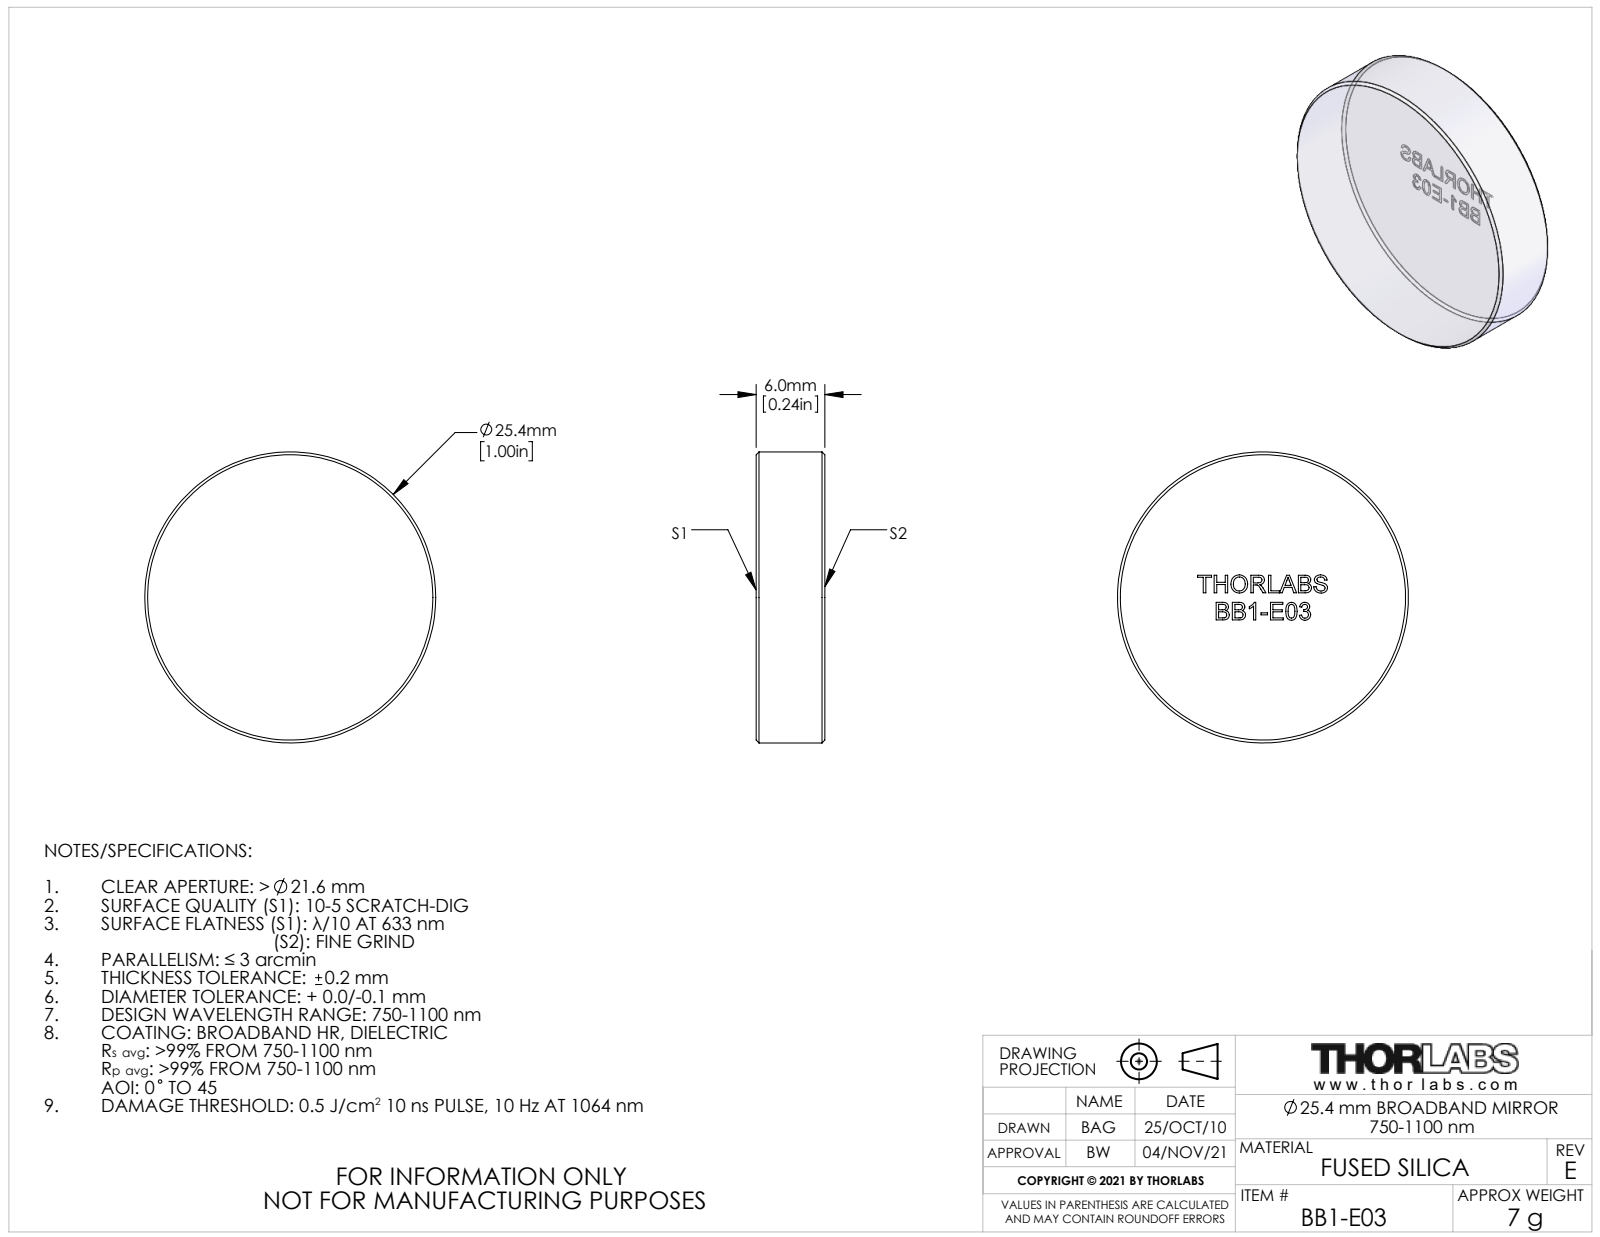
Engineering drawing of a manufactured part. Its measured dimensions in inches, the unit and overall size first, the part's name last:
Units: inches
Overall size (bounding box): 1 × 1 × 0.236
Round bosses / shafts (diameter × count): ⌀1 ×1
Main face-to-face distances: 0.236, 0.061, 0.093, 0.054, 0.155, 0.172, 0.033, 0.067, 0.047, 0.096
Volume: 0.185 in³ · Surface area: 2.276 in²
Bodies: 1 solid, 222 faces (128 planar, 2 cylindrical, 92 other)
Part name (STEP PRODUCT): 3544-E0W
STEP written by: SolidWorks 2016 (CONFIG_CONTROL_DESIGN)
